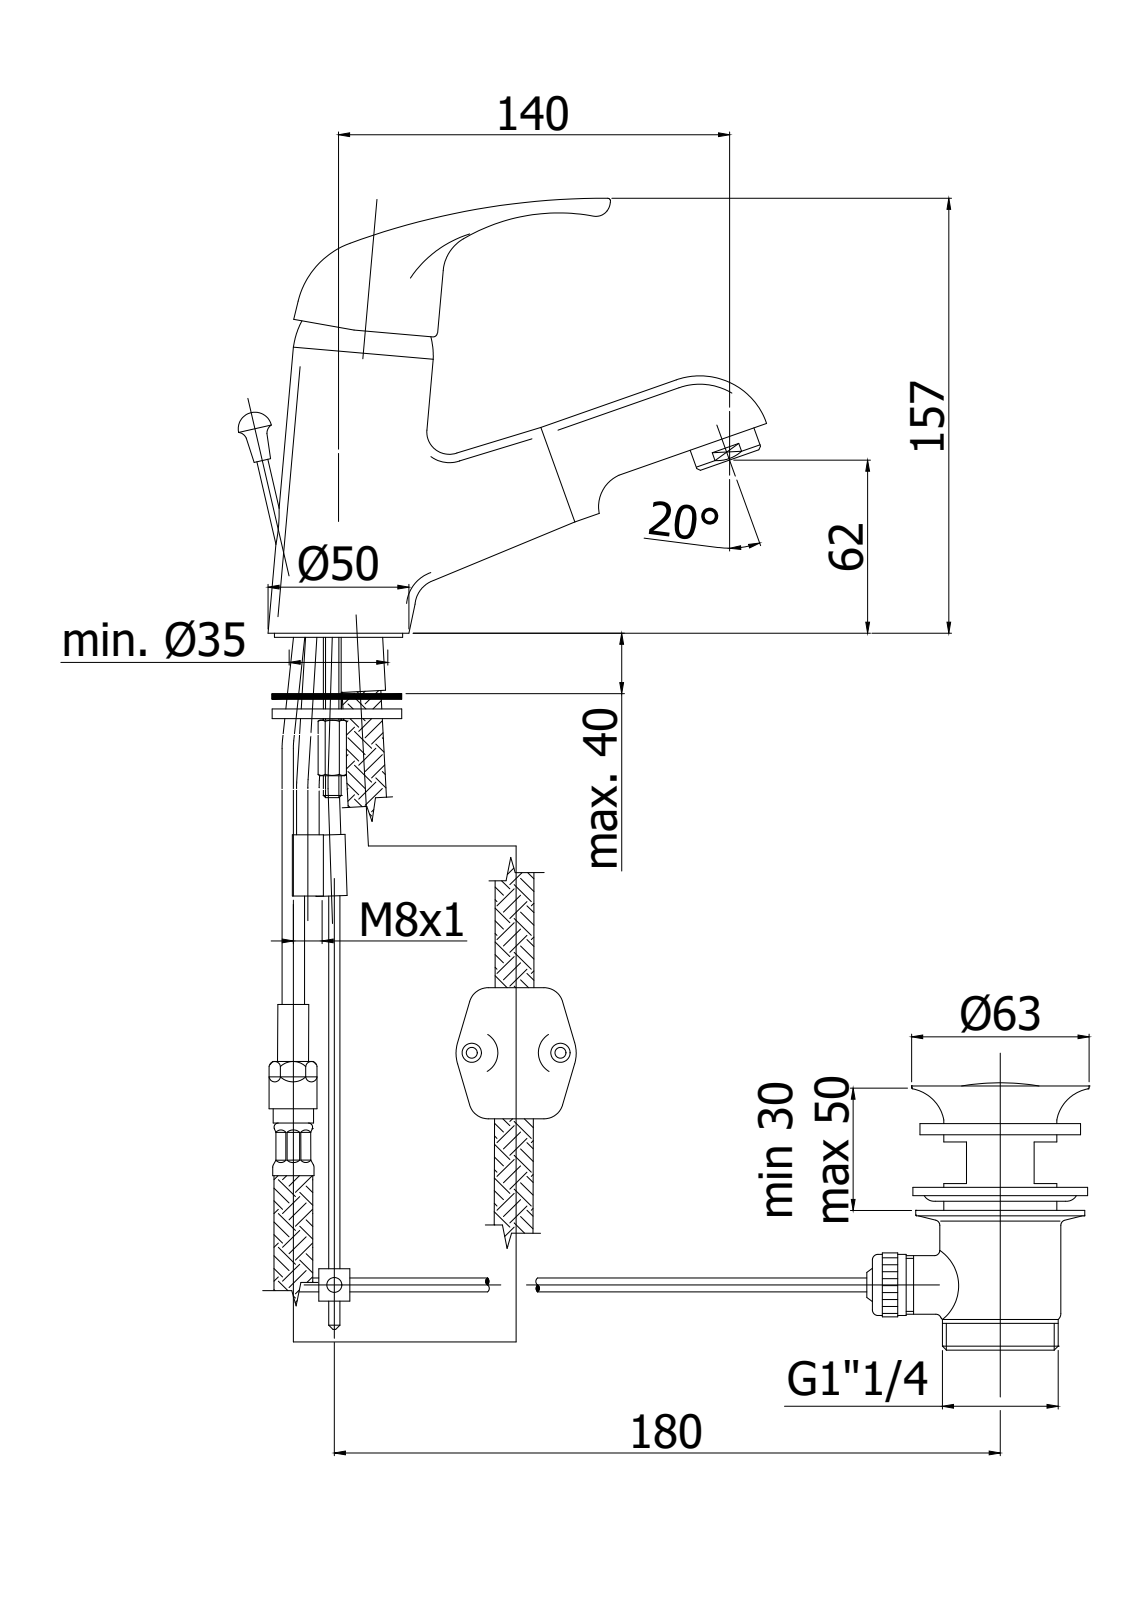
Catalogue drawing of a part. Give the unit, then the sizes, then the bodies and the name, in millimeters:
Units: millimetres
Overall size (bounding box): 188.2 × 162.04 × 57.8
Round holes (diameter × count): ⌀4.2 ×1, ⌀5 ×1, ⌀6 ×1, ⌀9.4 ×1, ⌀37 ×1, ⌀40 ×1, ⌀46.5 ×1, ⌀47 ×1
Round bosses / shafts (diameter × count): ⌀4 ×2, ⌀51 ×1, ⌀45.2 ×1, ⌀23.8 ×1, ⌀19 ×1
Partial cylindrical surfaces — rounded edges, fillets, slot ends (radius × count): R3.9 ×1, R4 ×1, R20 ×1
Main face-to-face distances: 7.3, 2.2, 5.1, 2.6, 12.7, 6.8, 4.6, 0.5, 33.24, 1
Volume: 396 664 mm³ · Surface area: 60 224 mm²
Bodies: 3 solids, 156 faces (61 planar, 35 cylindrical, 60 other)
Part name (STEP PRODUCT): ND072CR
STEP written by: CREO PARAMETRIC BY PTC INC, 2020044 (CONFIG_CONTROL_DESIGN)
